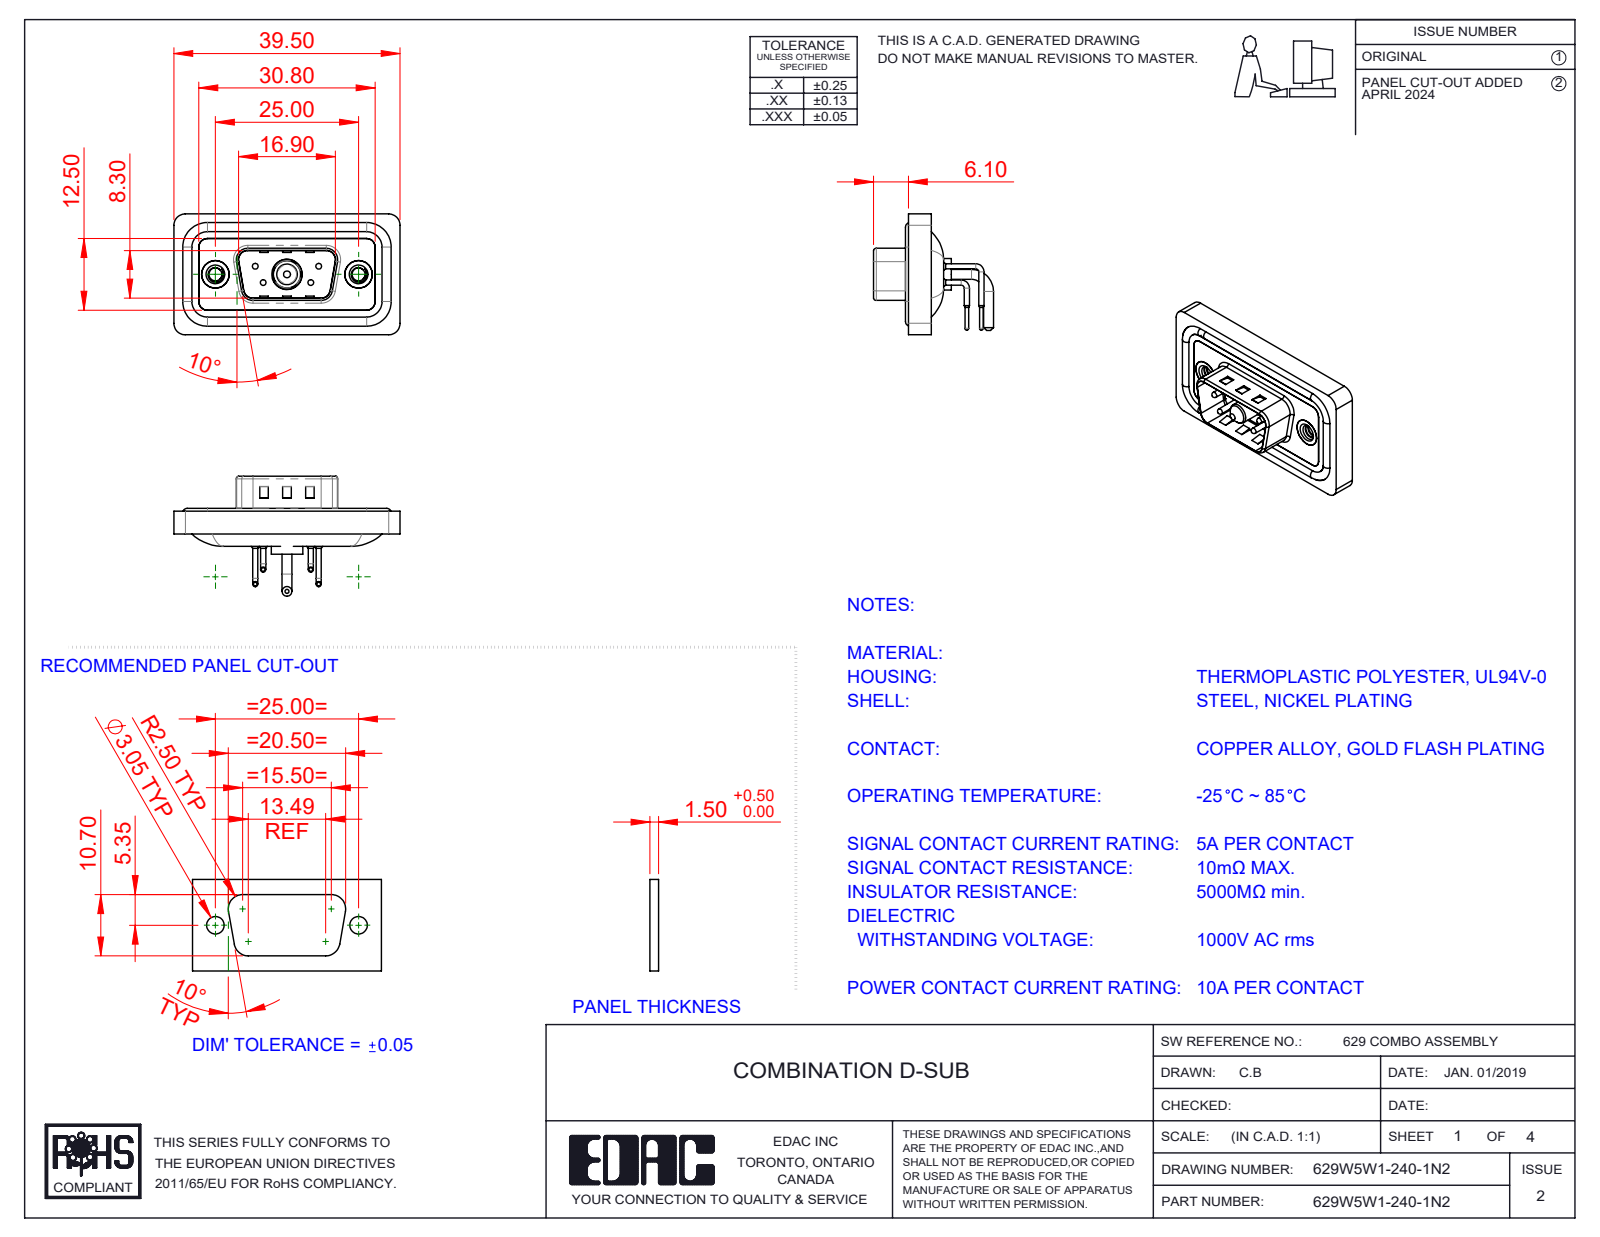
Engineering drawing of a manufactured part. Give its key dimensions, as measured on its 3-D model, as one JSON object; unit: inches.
{"part_name": "629Combo Threaded Rivet_2; 629Combo Contact Row 2; 629Combo Shell Rear_09 Contacts; 629Combo Housing_5W1 (+5 more)", "step_written_by": "SolidWorks 2023 (CONFIG_CONTROL_DESIGN)", "units": "inches", "bodies": {"solids": 13, "faces": 894, "planar": 411, "cylindrical": 345, "other": 138}, "overall_size": [1.555, 0.831, 0.825], "volume_in3": 0.27, "surface_area_in2": 11.03, "round_holes": [[0.03, 4], [0.063, 4], [0.079, 4], [0.089, 2], [0.157, 2], [0.189, 2], [0.197, 2], [0.191, 1], [0.209, 1]], "round_bosses_or_shafts": [[0.035, 8], [0.063, 4], [0.059, 4], [0.039, 4], [0.026, 4], [0.193, 2], [0.067, 2], [0.217, 1]], "partial_cylinders_radius": [[0.059, 18], [0.079, 18], [0.02, 8], [0.063, 8], [0.01, 4], [0.024, 4], [0.026, 4], [0.035, 4]], "face_to_face_distances": [0.016, 0.114, 0.043, 0.031, 0.083, 0.098, 0.063, 0.122, 0.059, 0.177], "hole_center_spacings": [0.124, 0.225, 0.28, 0.492, 0.713, 0.173, 0.173, 0.327]}
